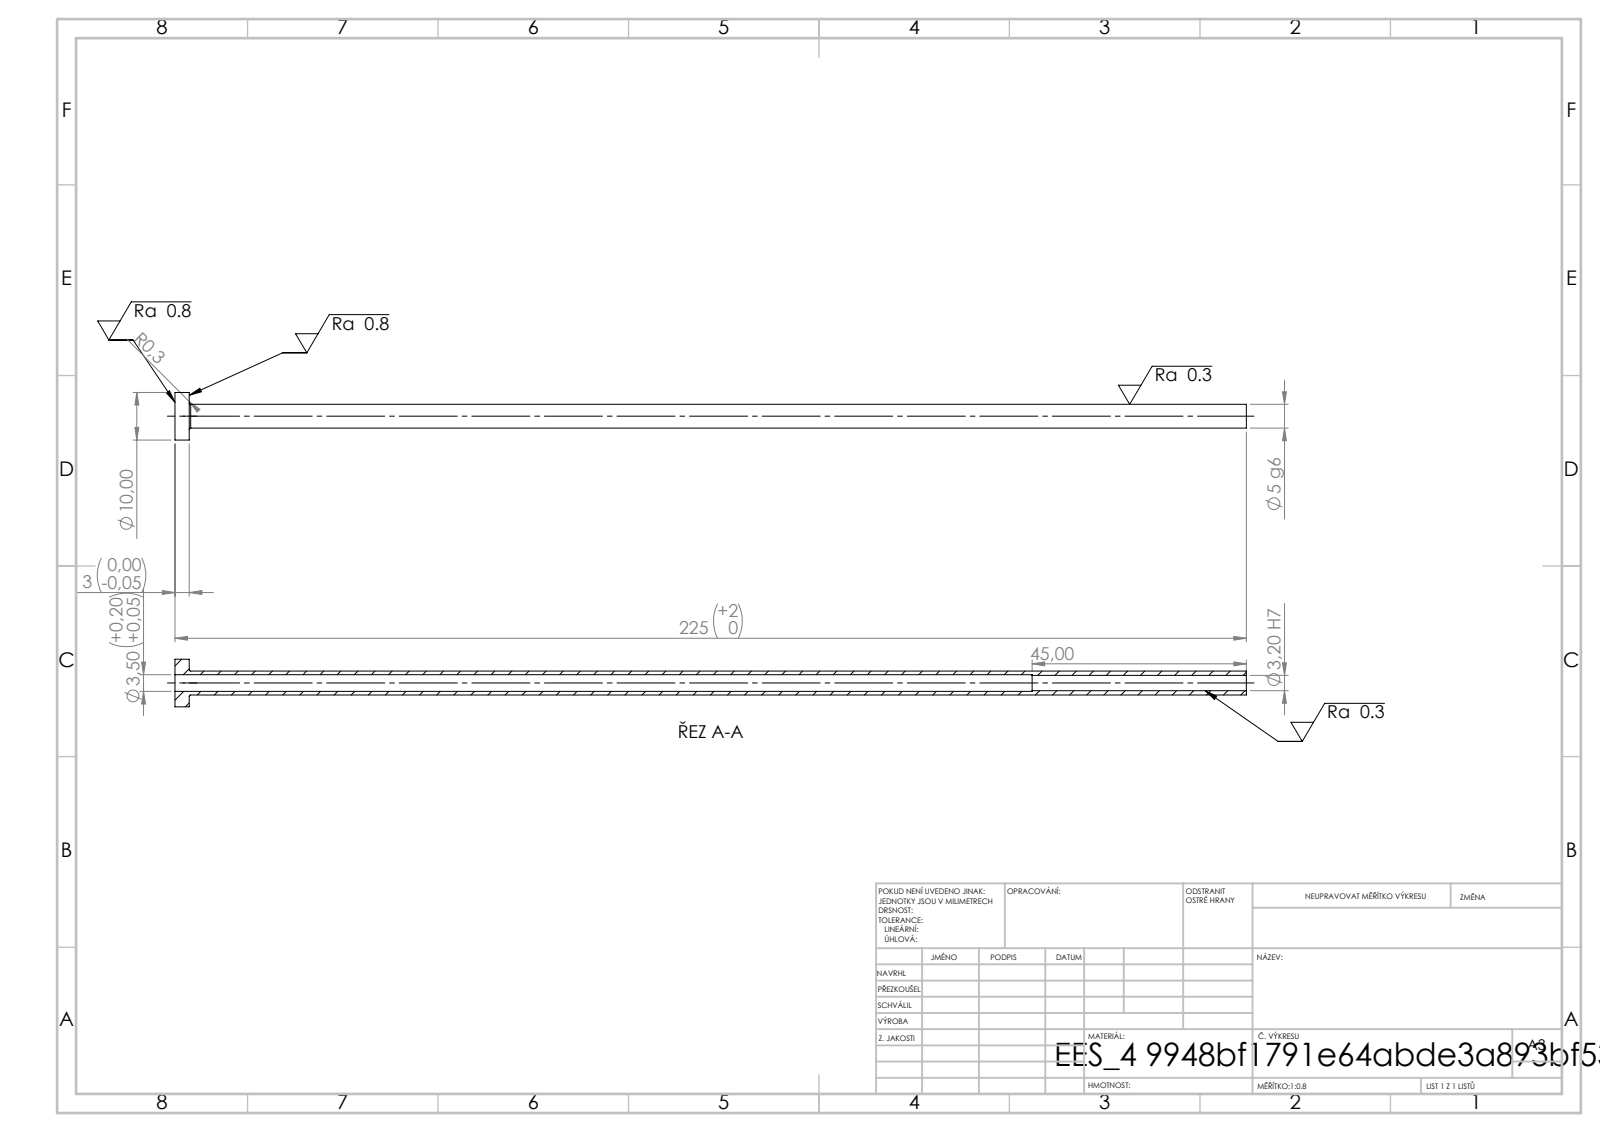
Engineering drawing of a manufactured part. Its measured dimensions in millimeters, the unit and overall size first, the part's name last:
Units: millimetres
Overall size (bounding box): 225 × 10 × 10
Round holes (diameter × count): ⌀3.2 ×1, ⌀3.5 ×1
Round bosses / shafts (diameter × count): ⌀10 ×1, ⌀5 ×1
Main face-to-face distances: 3, 225, 222, 180, 177, 45
Volume: 2 501 mm³ · Surface area: 6 152 mm²
Bodies: 1 solid, 14 faces (4 planar, 8 cylindrical, 2 other)
STEP written by: SolidWorks 2019 (CONFIG_CONTROL_DESIGN)
